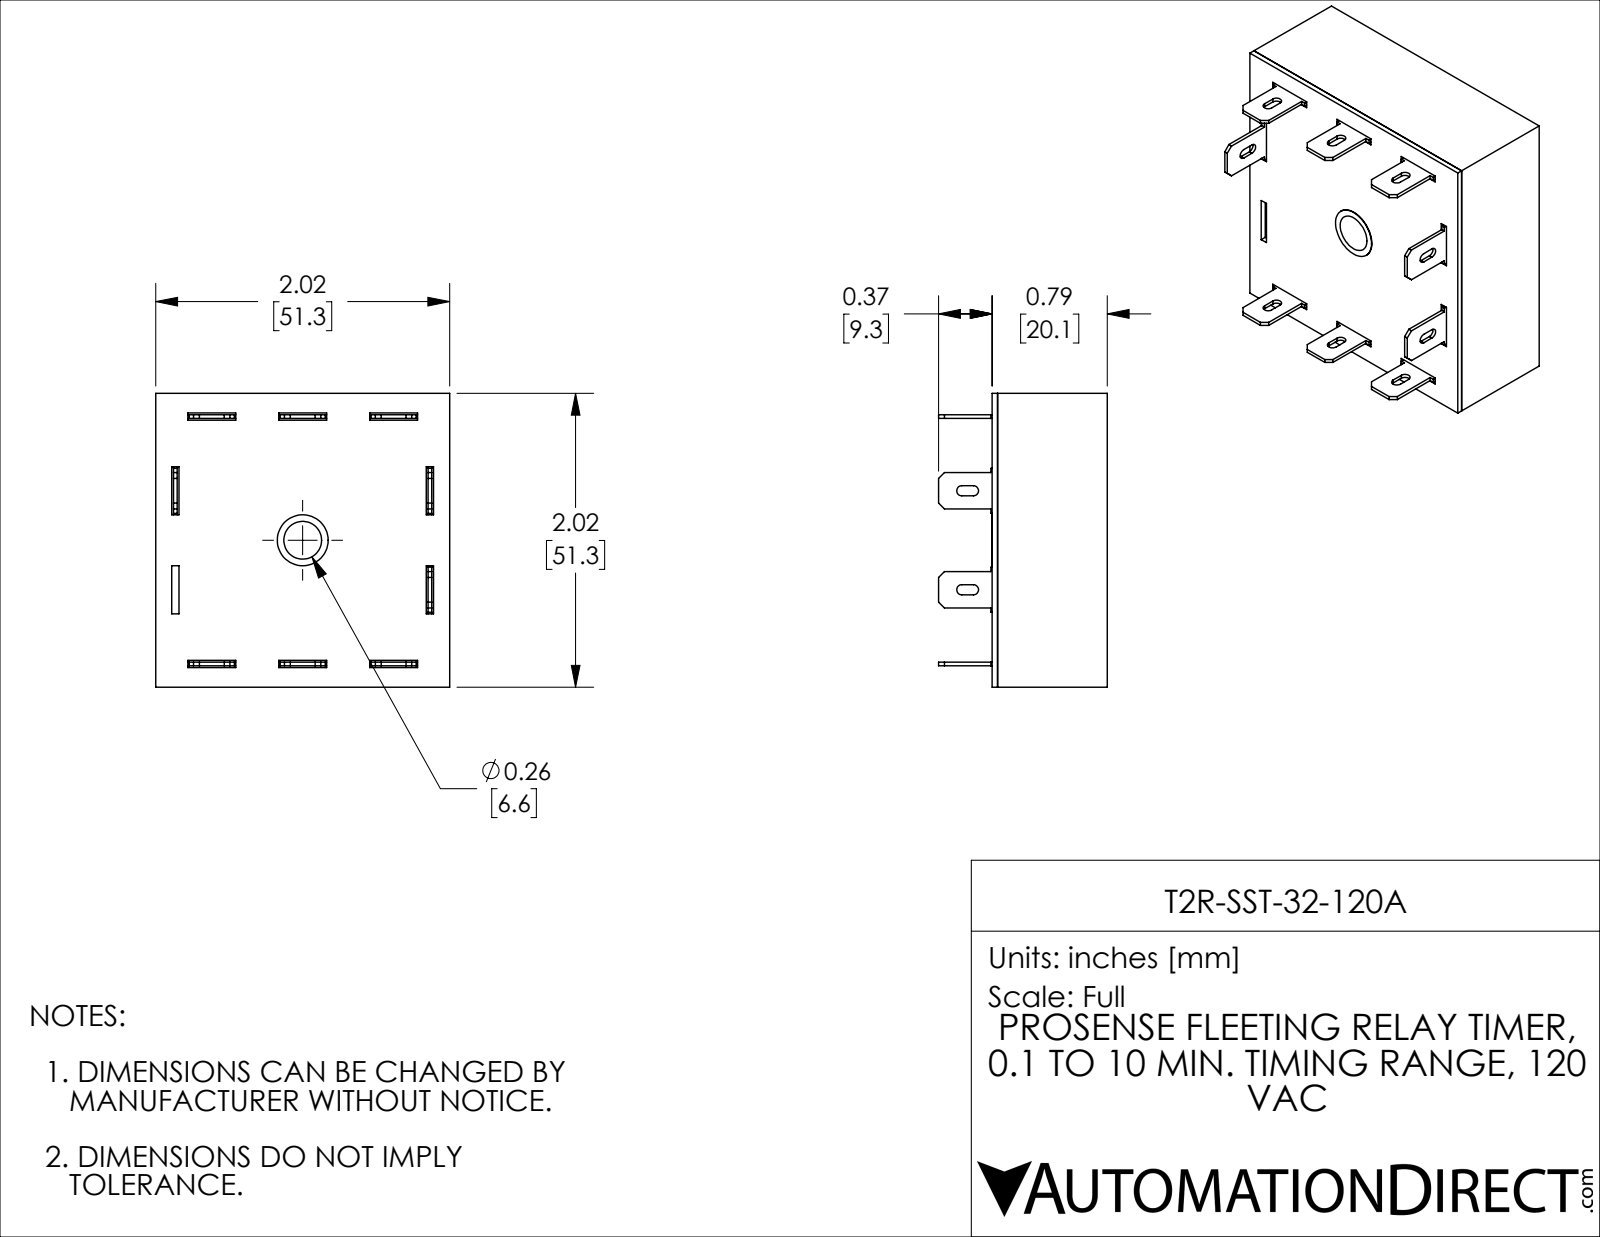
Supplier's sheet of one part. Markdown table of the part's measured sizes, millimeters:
| quantity | value |
| --- | --- |
| part name | T2R-SST-32-120A |
| STEP written by | SolidWorks 2021 (CONFIG_CONTROL_DESIGN) |
| units | millimeters |
| bodies | 11 solids, 280 faces (256 planar, 22 cylindrical, 2 other) |
| overall size | 51.31 × 51.31 × 29.46 |
| volume | 11 178 mm³ |
| surface area | 23 301 mm² |
| round holes (diameter × count) | 8.89 × 1 |
| partial cylindrical surfaces (radius × count) | 0.89 × 10 |
| main face-to-face distances | 1.14, 50.16, 19.15, 20.12, 0.97, 18.01, 18.98, 51.3, 3.74, 47.56 |
